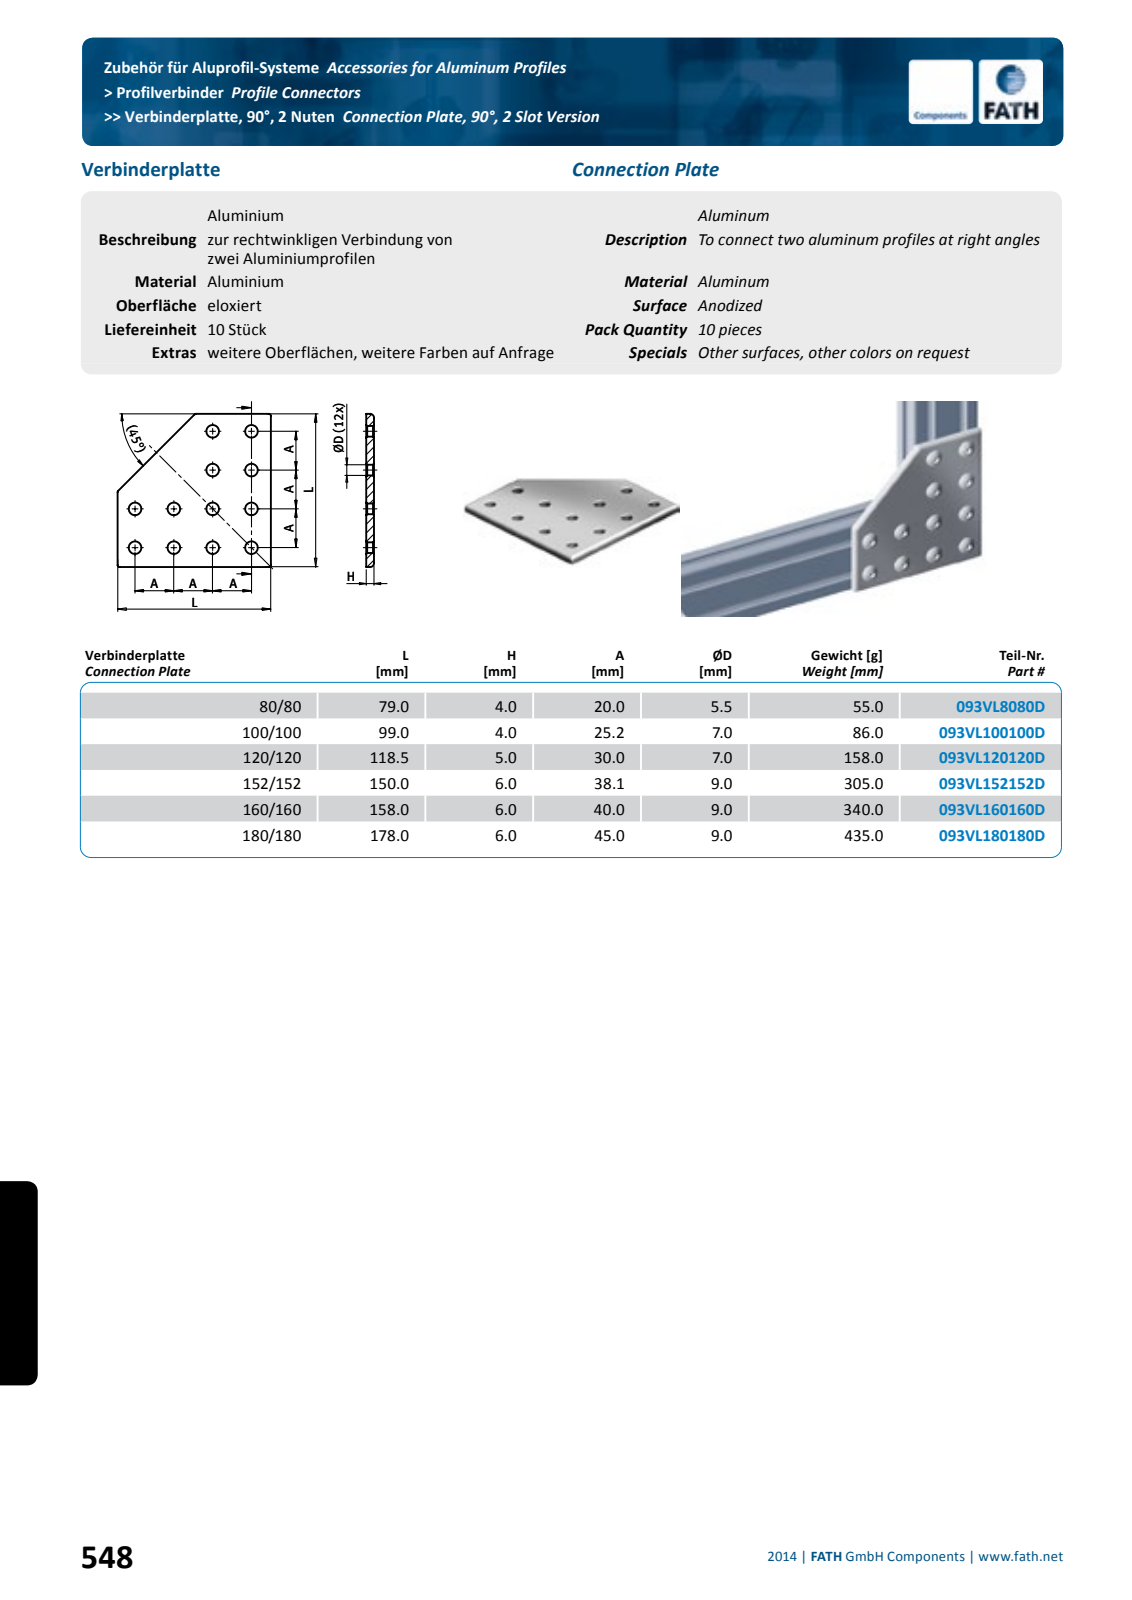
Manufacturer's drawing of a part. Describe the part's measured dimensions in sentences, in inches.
The part is named "fath_093vl180180d". Its 3-D file was written by "Spatial InterOp 3D (automotive_design)". It is 1 solid with 94 faces: 7 planar, 34 cylindrical and 53 other. Overall it measures 7.008 by 7.008 by 0.236 inches. Its volume is 9.798 cubic inches and its surface area 91.38 square inches. Round holes: 12 of diameter 0.354. Partial cylindrical surfaces (rounded edges, fillets, slot ends): 10 of radius 0.079. The main face-to-face distances are 0.236, 7.008. The hole center spacings are 1.772, 3.961, 2.506, 3.543, 5.602, 5.011, 5.315, 6.388.
